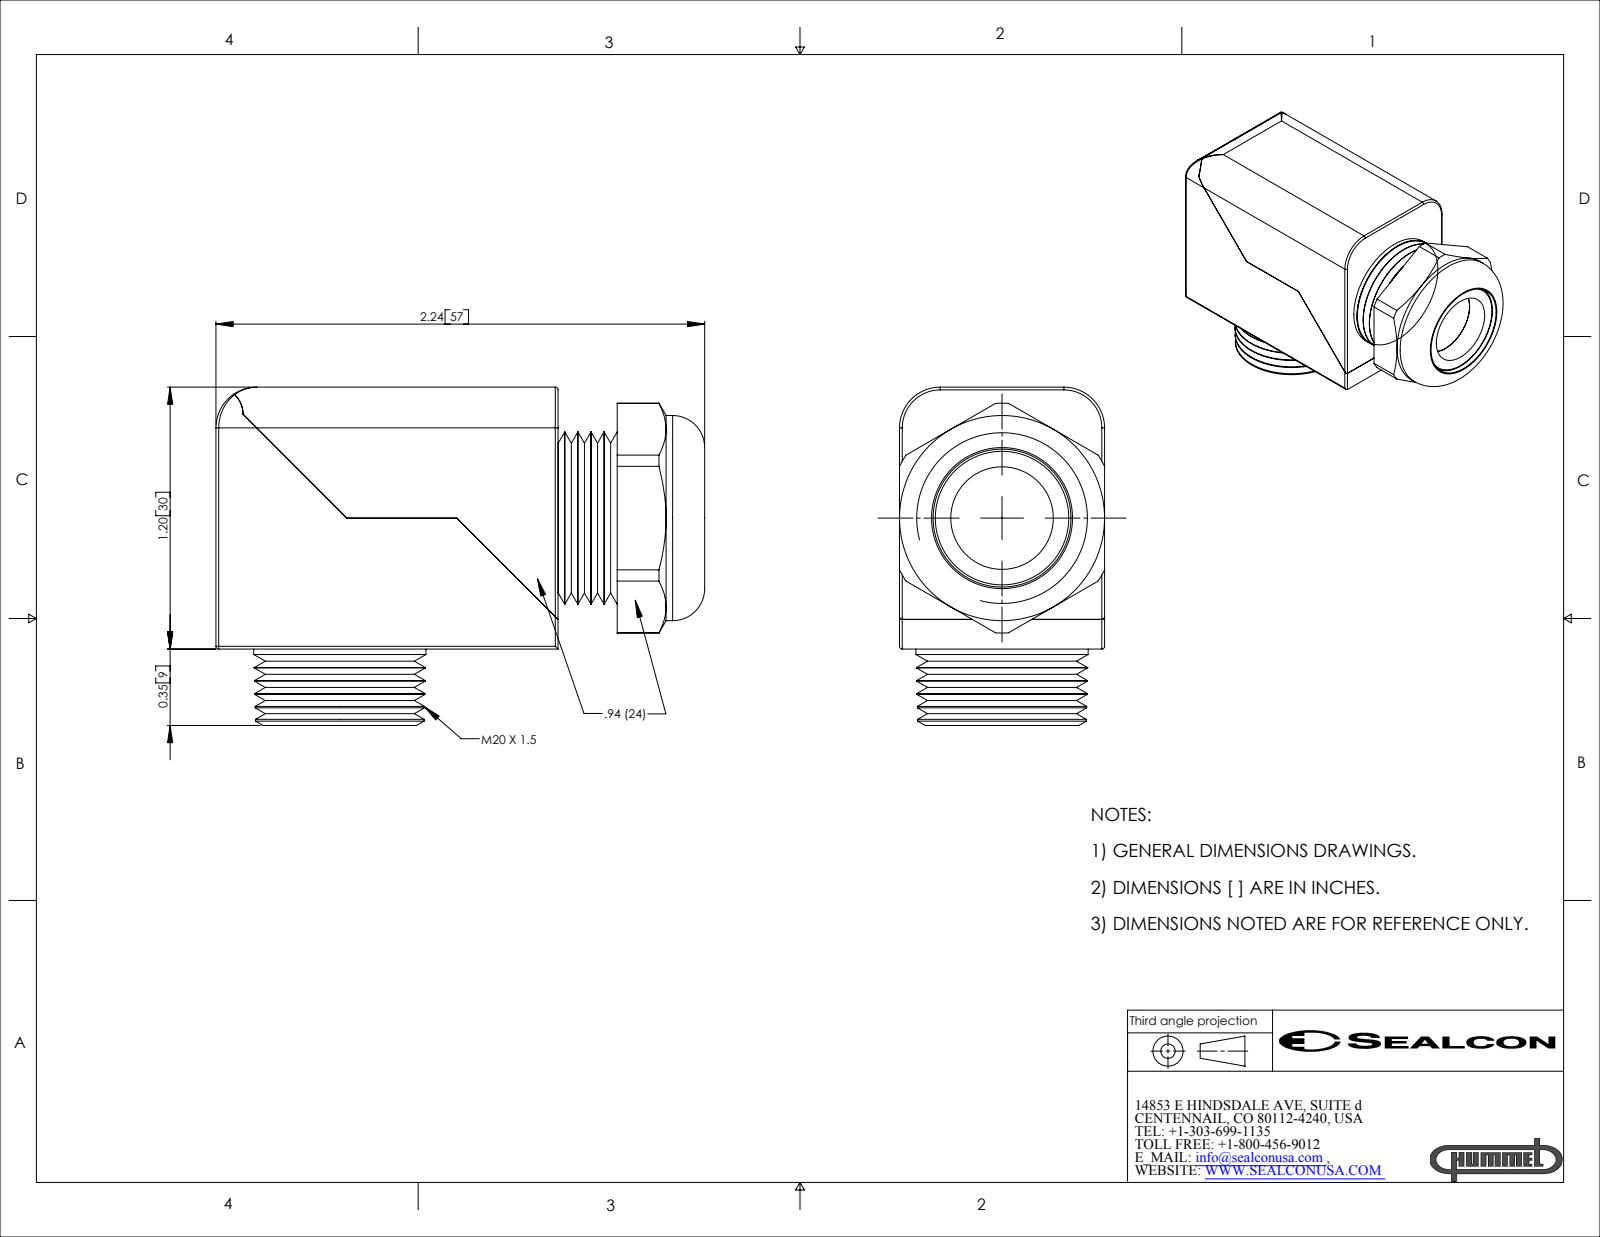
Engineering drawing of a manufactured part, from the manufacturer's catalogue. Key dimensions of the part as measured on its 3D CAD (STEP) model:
Part name (STEP PRODUCT): ED20MA-BK
STEP written by: SolidWorks 2007 (CONFIG_CONTROL_DESIGN)
Units: inches
Bodies: 3 solids, 151 faces (29 planar, 48 cylindrical, 74 other)
Overall size (bounding box): 2.24 × 1.55 × 0.94
Volume: 1.82 in³ · Surface area: 20.04 in²
Round holes (diameter × count): ⌀0.47 ×2, ⌀0.632 ×1
Round bosses / shafts (diameter × count): ⌀0.94 ×1, ⌀0.79 ×1
Partial cylindrical surfaces — rounded edges, fillets, slot ends (radius × count): R0.013 ×8, R0.187 ×3, R0.124 ×1, R0.526 ×1
Main face-to-face distances: 0.94, 0.356, 0.6, 1.2, 1.568, 0.495, 2.063, 0.224, 0.271, 1.839
